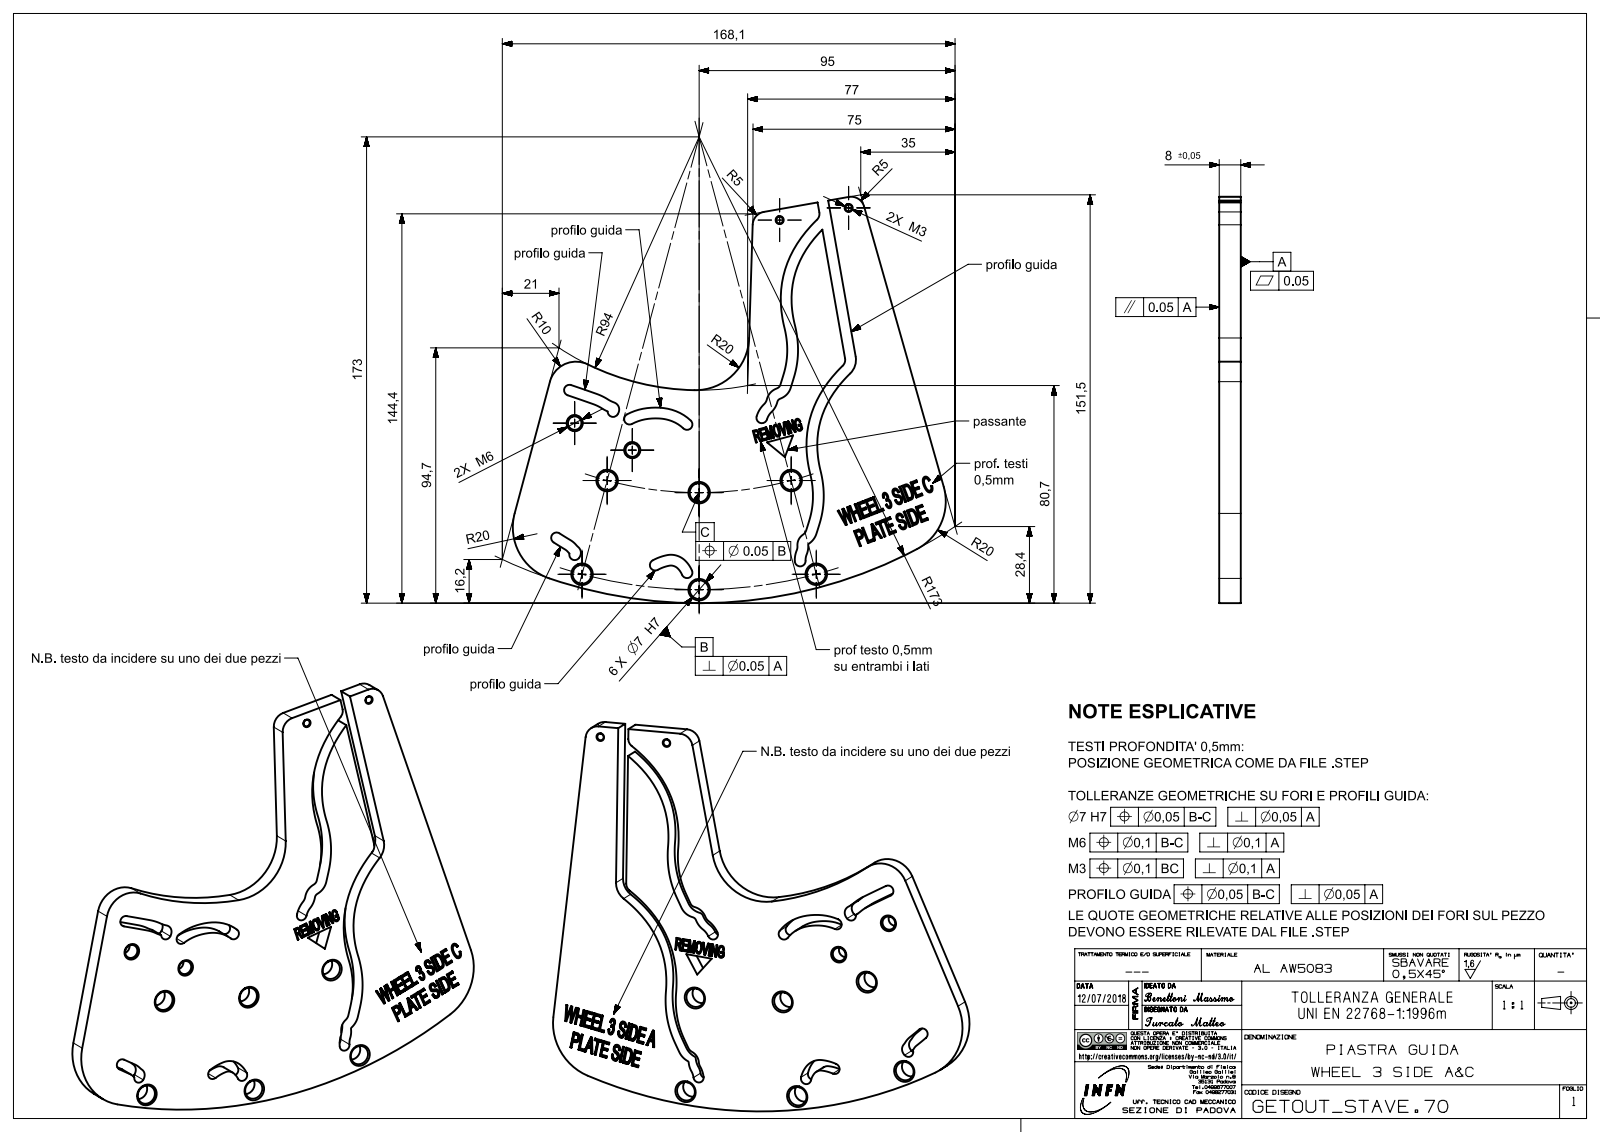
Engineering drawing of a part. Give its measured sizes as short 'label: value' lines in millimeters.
name: turc155078D8vtfp
written by: SIEMENS PLM Software NX 12.0 (AP203_CONFIGURATION_CONTROLLED_3D_DESIGN_OF_MECHANICAL_PARTS_AND_ASSEMBLIES_MIM_LF)
unit: mm
bodies: 1 solid, 624 faces (469 planar, 31 cylindrical, 124 other)
size: 166.08 × 138.44 × 8
volume: 106 905 mm³; area: 38 446 mm²
holes: 6× ⌀7, 2× ⌀2.5, 2× ⌀5
rounds: 10× R2, 3× R20, 2× R3, 2× R5, 1× R7, 1× R10, 1× R94, 1× R173
face distances: 8, 4.02, 0.5, 7.5, 7, 1, 6.5, 6, 9.21, 4
hole spacings: 52.98, 34.46, 36, 14.63, 23.6, 24.47, 26, 29.43
